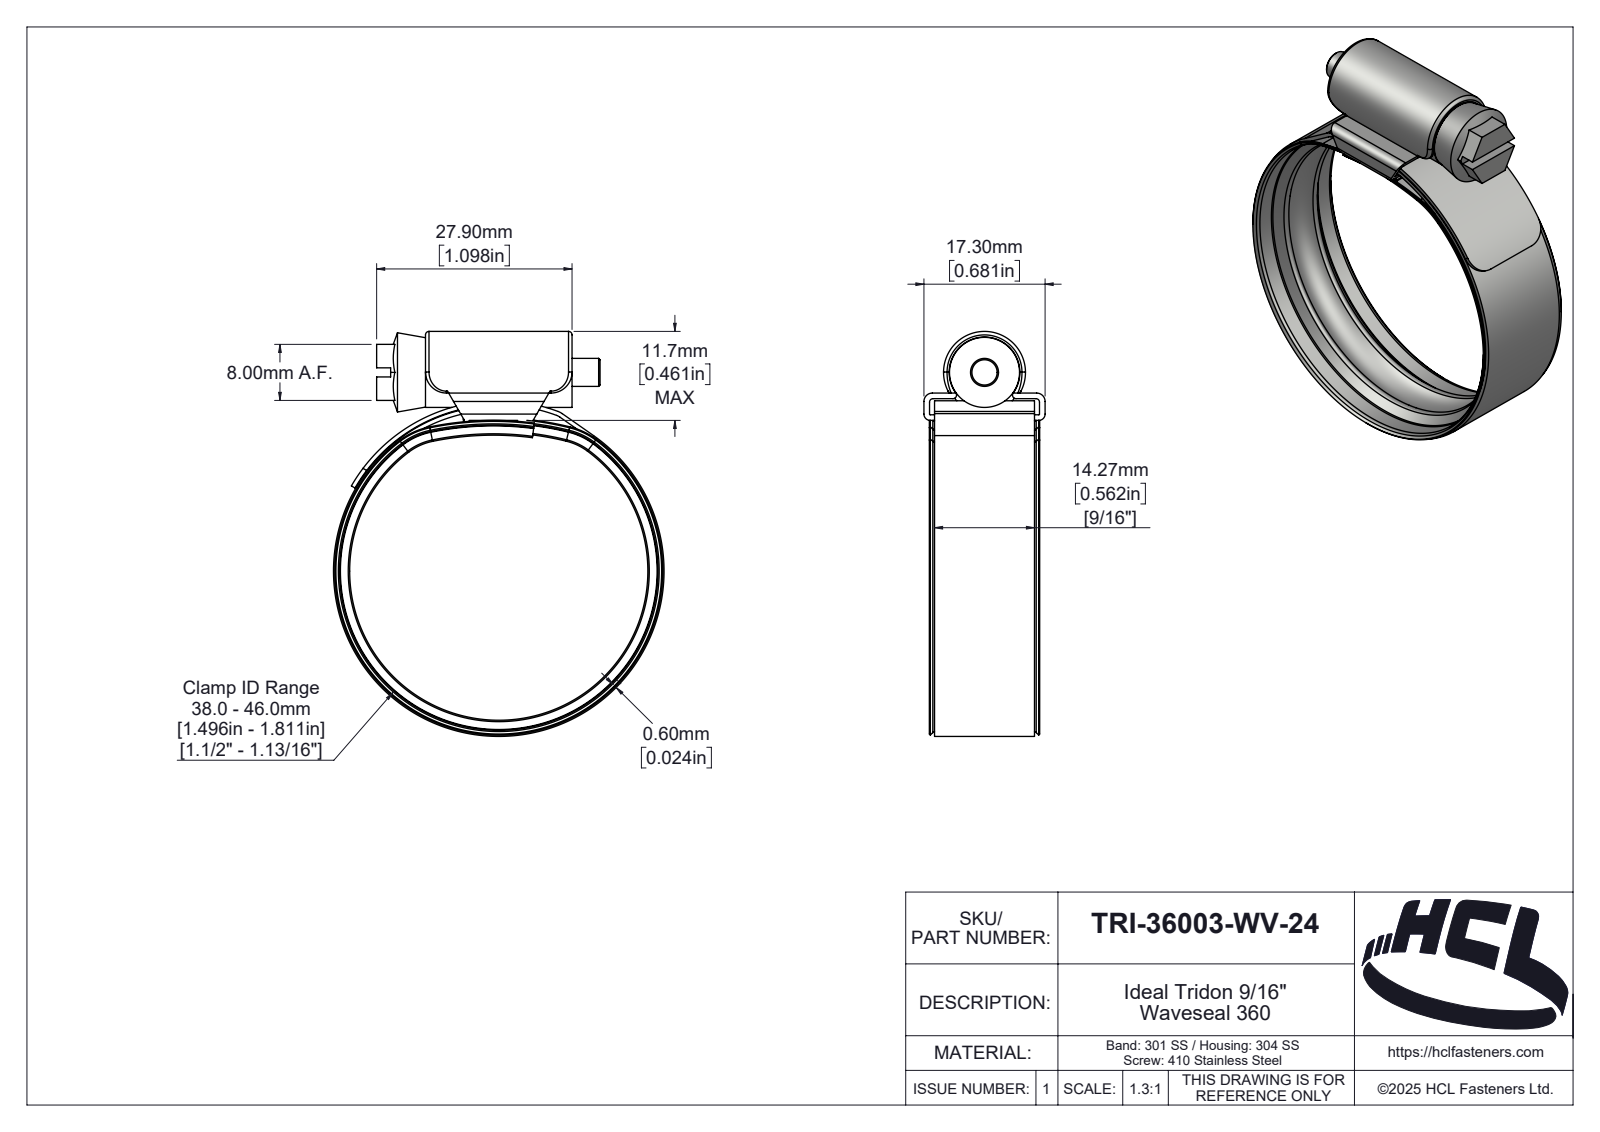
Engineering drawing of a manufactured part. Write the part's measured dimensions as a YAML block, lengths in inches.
part_name: "TRI-36003-WV-24"
step_written_by: "SolidWorks 2025 (AUTOMOTIVE_DESIGN)"
units: inches
bodies: {solids: 4, faces: 418, planar: 42, cylindrical: 119, other: 257}
overall_size: [2.276, 1.858, 0.681]
volume: 0.296
surface_area: 20.6
round_holes:
  - {diameter: 1.787, count: 1}
  - {diameter: 1.811, count: 1}
round_bosses_or_shafts:
  - {diameter: 1.858, count: 1}
  - {diameter: 1.803, count: 1}
  - {diameter: 0.394, count: 1}
  - {diameter: 0.157, count: 1}
partial_cylinders:
  - {radius: 0.02, count: 6}
  - {radius: 0.118, count: 4}
  - {radius: 0.004, count: 2}
  - {radius: 0.035, count: 2}
  - {radius: 0.047, count: 2}
  - {radius: 0.39, count: 2}
  - {radius: 0.398, count: 2}
  - {radius: 0.018, count: 1}
face_to_face_distances: [0.031, 0.122, 0.561, 0.091, 0.024, 0.154, 1.098, 0.06, 0.621, 0.65]
